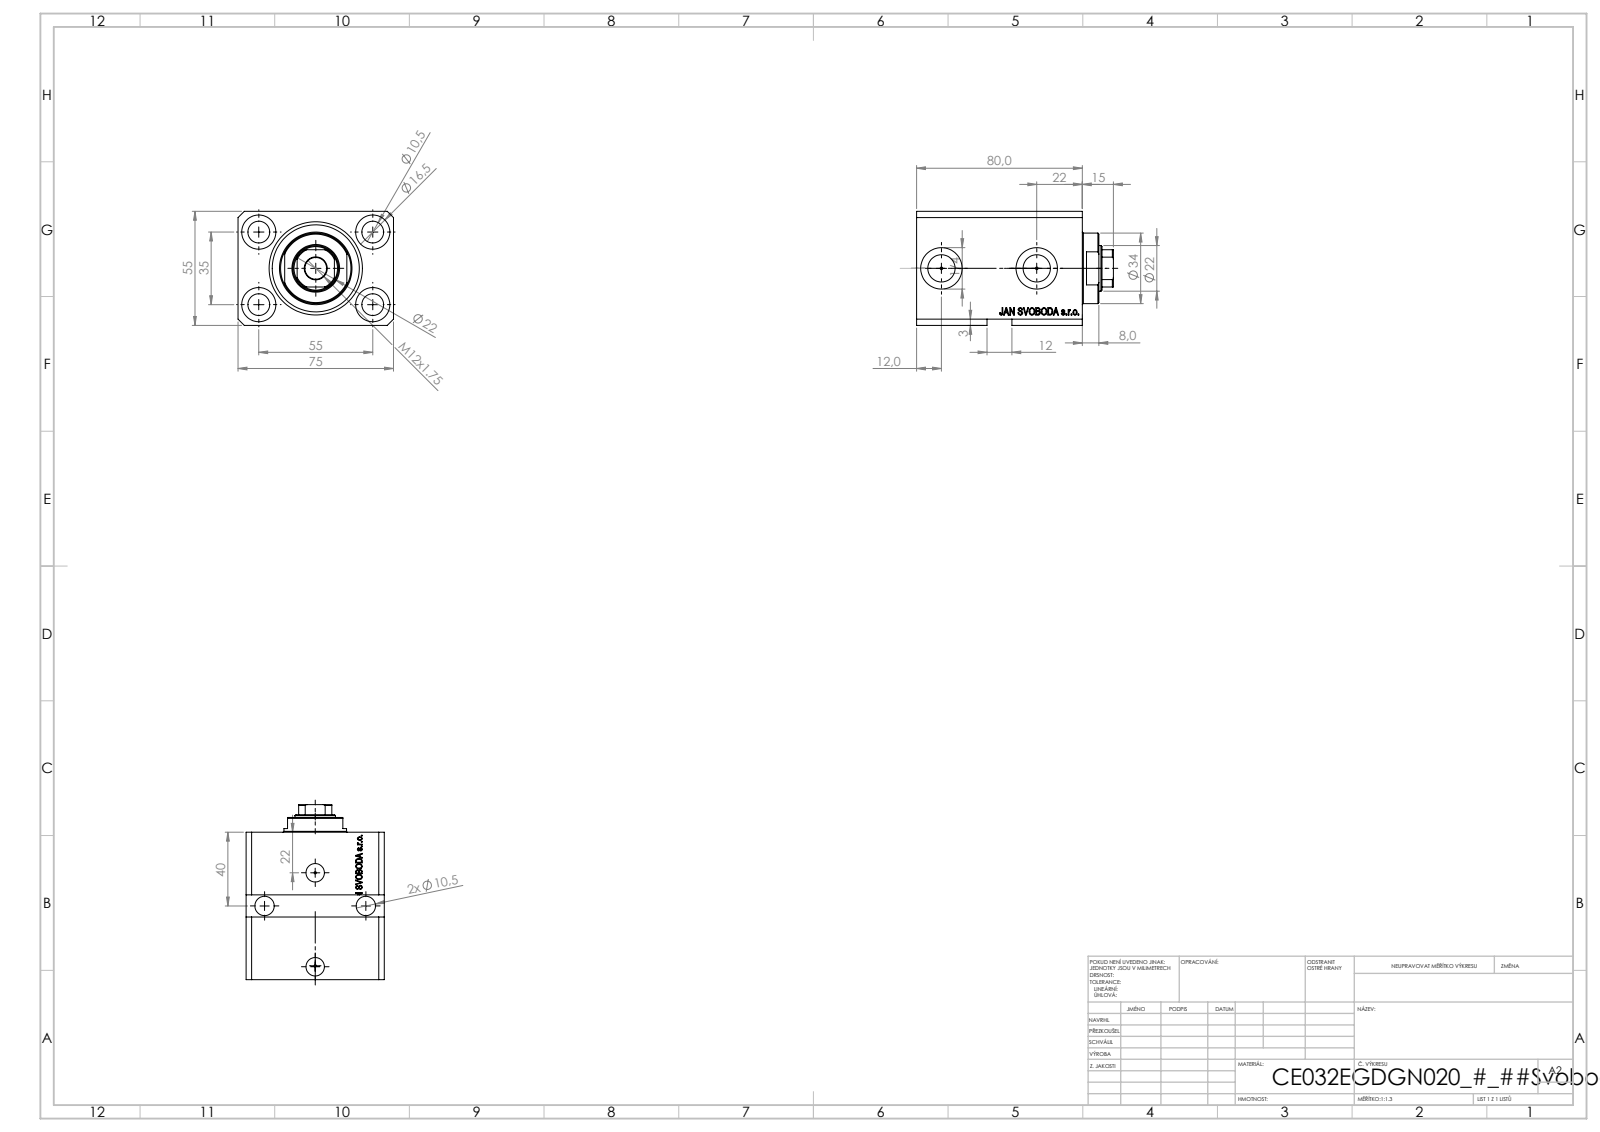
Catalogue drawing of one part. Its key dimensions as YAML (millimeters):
part_name: "V250CE_E_Body; V250CE_C_VCP; V250CE_VC_E"
step_written_by: "SolidWorks 2019 (CONFIG_CONTROL_DESIGN)"
units: millimeters
bodies: {solids: 3, faces: 910, planar: 442, cylindrical: 96, other: 372}
overall_size: [95, 75, 55]
volume: 271835
surface_area: 68383
round_holes:
  - {diameter: 10.5, count: 7}
  - {diameter: 1.25, count: 4}
  - {diameter: 16.5, count: 4}
  - {diameter: 10, count: 2}
  - {diameter: 13.16, count: 2}
  - {diameter: 20, count: 2}
  - {diameter: 22, count: 1}
  - {diameter: 32, count: 1}
  - {diameter: 45, count: 1}
round_bosses_or_shafts:
  - {diameter: 34, count: 1}
partial_cylinders:
  - {radius: 10.5, count: 1}
face_to_face_distances: [55, 75, 15, 80, 65, 9.9, 55.1, 70.1, 11, 69]
hole_center_spacings: [32.6, 55, 32.87, 35, 42.55, 42.96, 65.19, 0.53]
